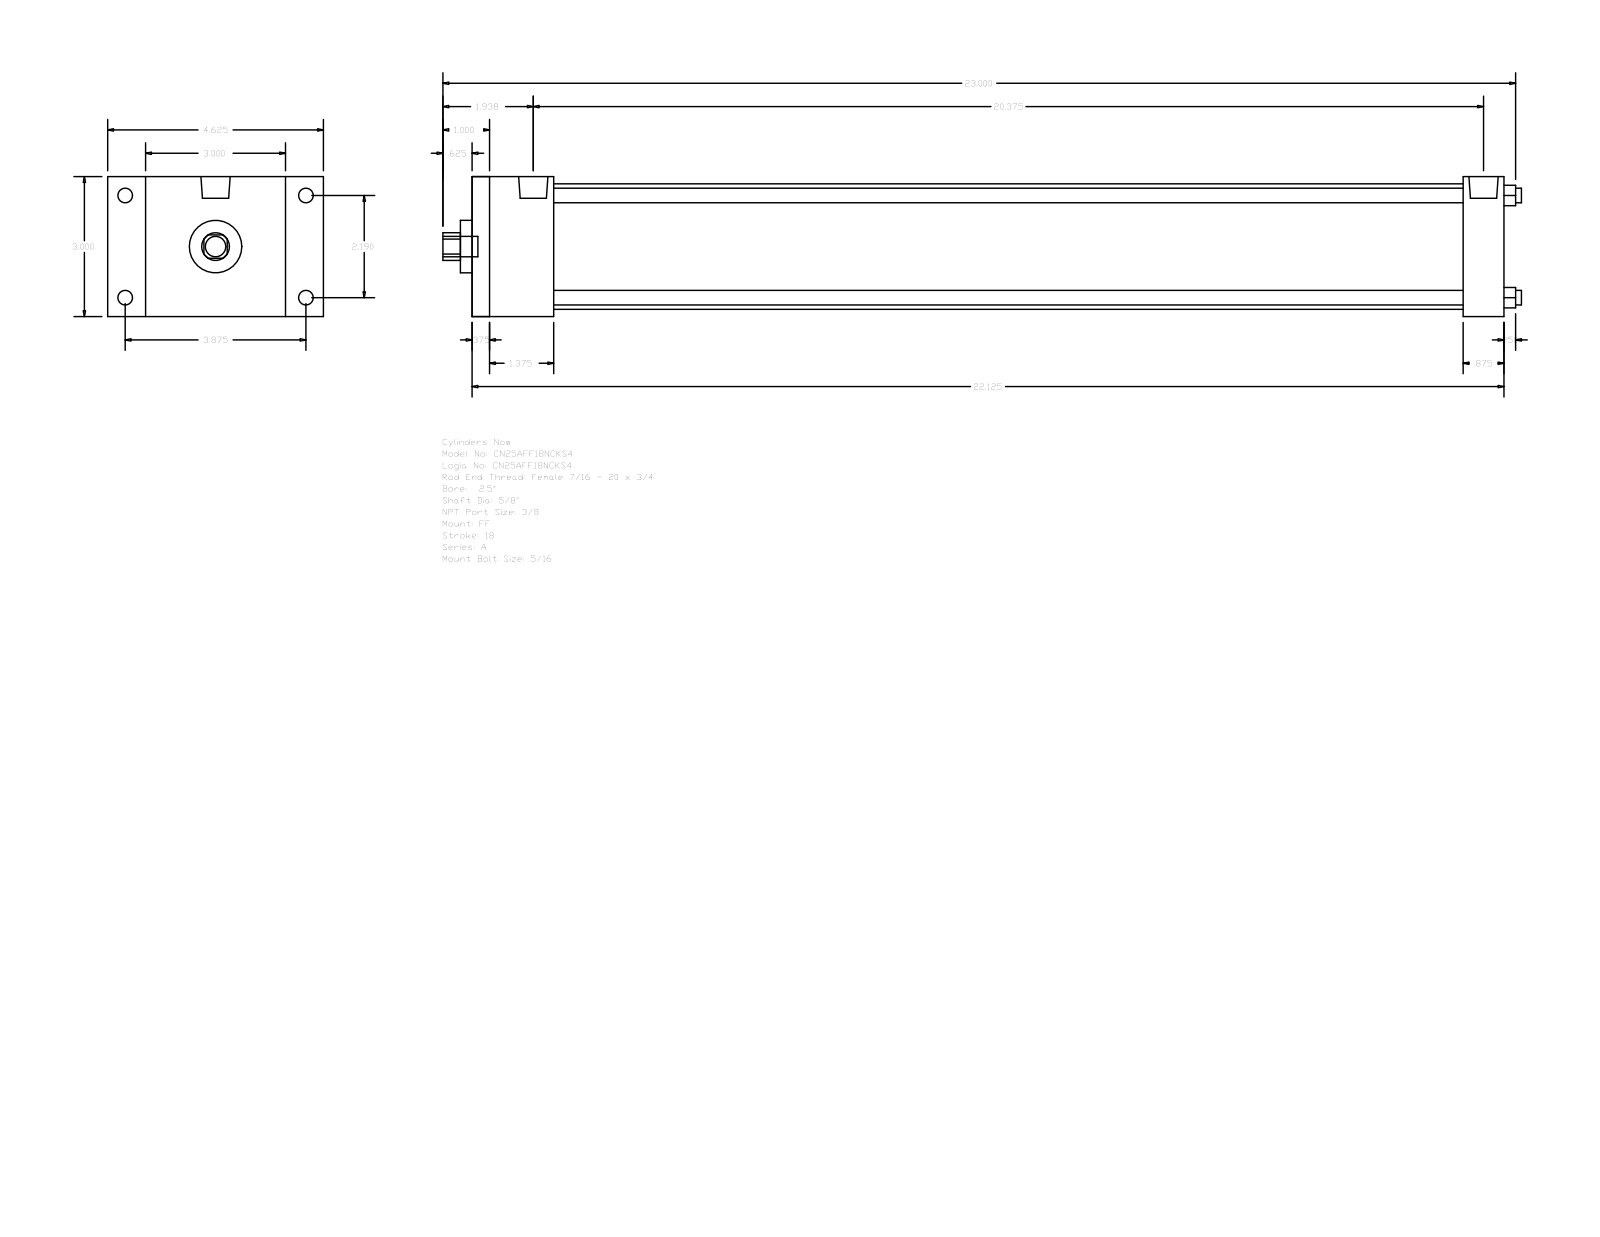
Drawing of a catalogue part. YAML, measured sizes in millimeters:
part_name: "A_FF__0250_0.625"
step_written_by: "GSSL Pune (CONFIG_CONTROL_DESIGN)"
units: millimeters
bodies: {solids: 0, faces: 92, planar: 64, cylindrical: 28, other: 0}
overall_size: [587.38, 117.47, 76.2]
round_holes:
  - {diameter: 7.94, count: 4}
  - {diameter: 15.88, count: 1}
  - {diameter: 28.57, count: 1}
  - {diameter: 68.33, count: 1}
round_bosses_or_shafts:
  - {diameter: 7.94, count: 4}
  - {diameter: 5.56, count: 4}
  - {diameter: 15.93, count: 2}
  - {diameter: 11.11, count: 1}
partial_cylinders:
  - {radius: 7.54, count: 1}
face_to_face_distances: [76.2, 561.97, 9.52, 552.45, 44.45, 539.74, 34.93, 530.22, 495.29, 517.52]
hole_center_spacings: [39.33, 55.62, 78.66]
